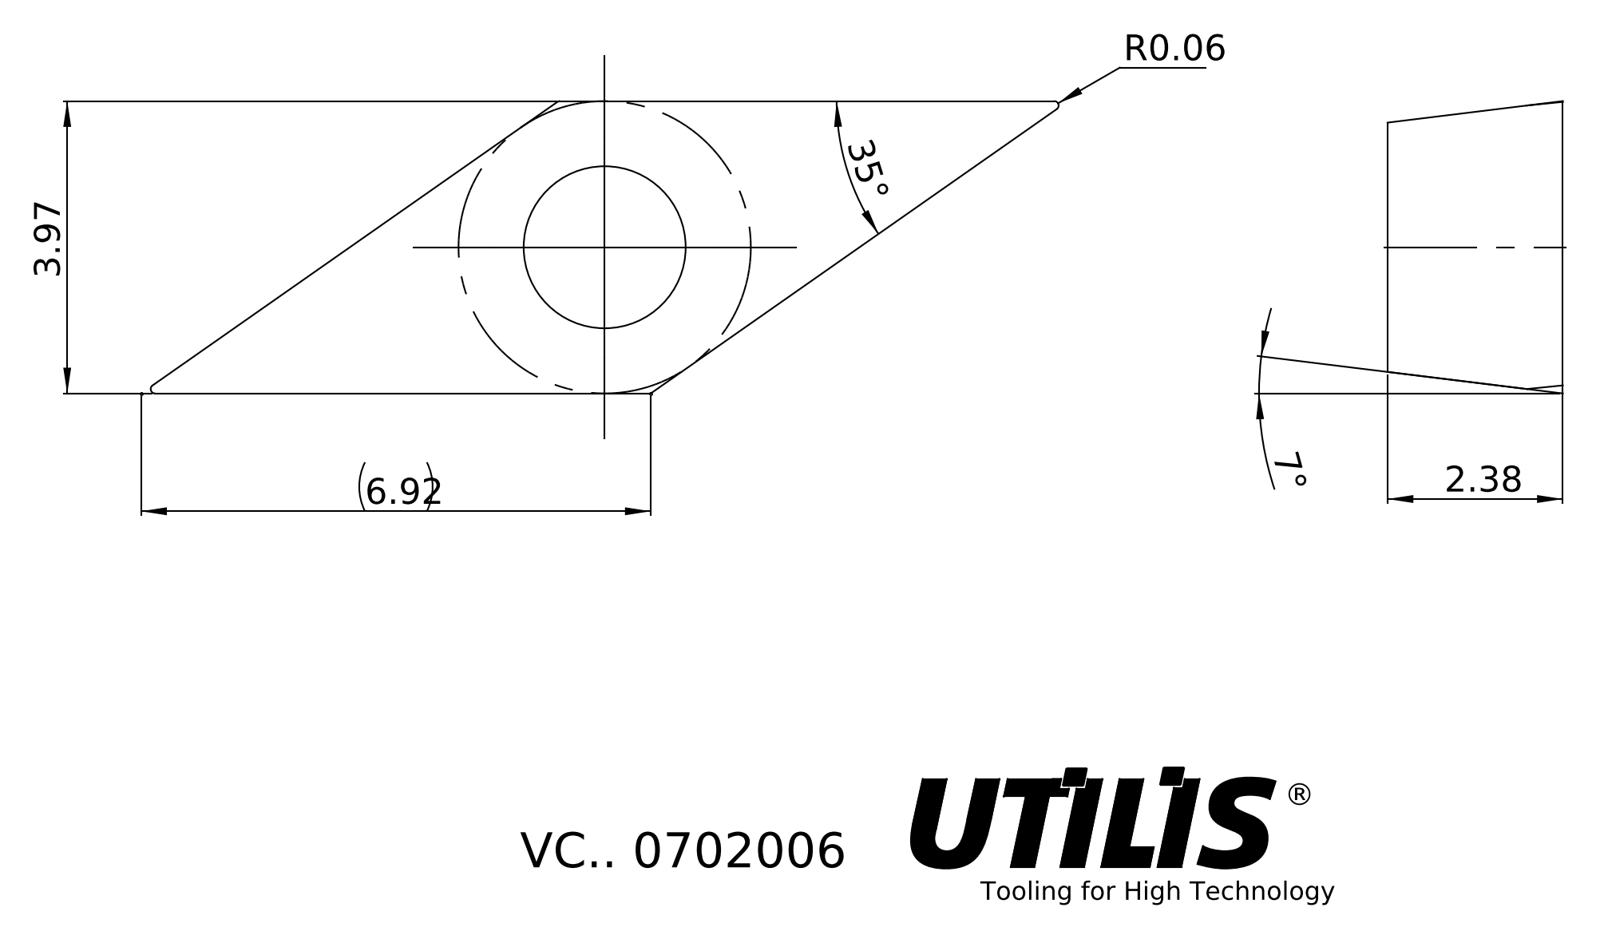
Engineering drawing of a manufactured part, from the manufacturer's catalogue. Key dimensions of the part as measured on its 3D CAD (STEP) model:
Part name (STEP PRODUCT): VC.. 0702006
STEP written by: SolidWorks 2016 (AUTOMOTIVE_DESIGN)
Units: millimetres
Bodies: 1 solid, 13 faces (2 planar, 2 cylindrical, 9 other)
Overall size (bounding box): 12.33 × 3.97 × 2.38
Volume: 47 mm³ · Surface area: 118 mm²
Round holes (diameter × count): ⌀2.2 ×1
Main face-to-face distances: 2.38
